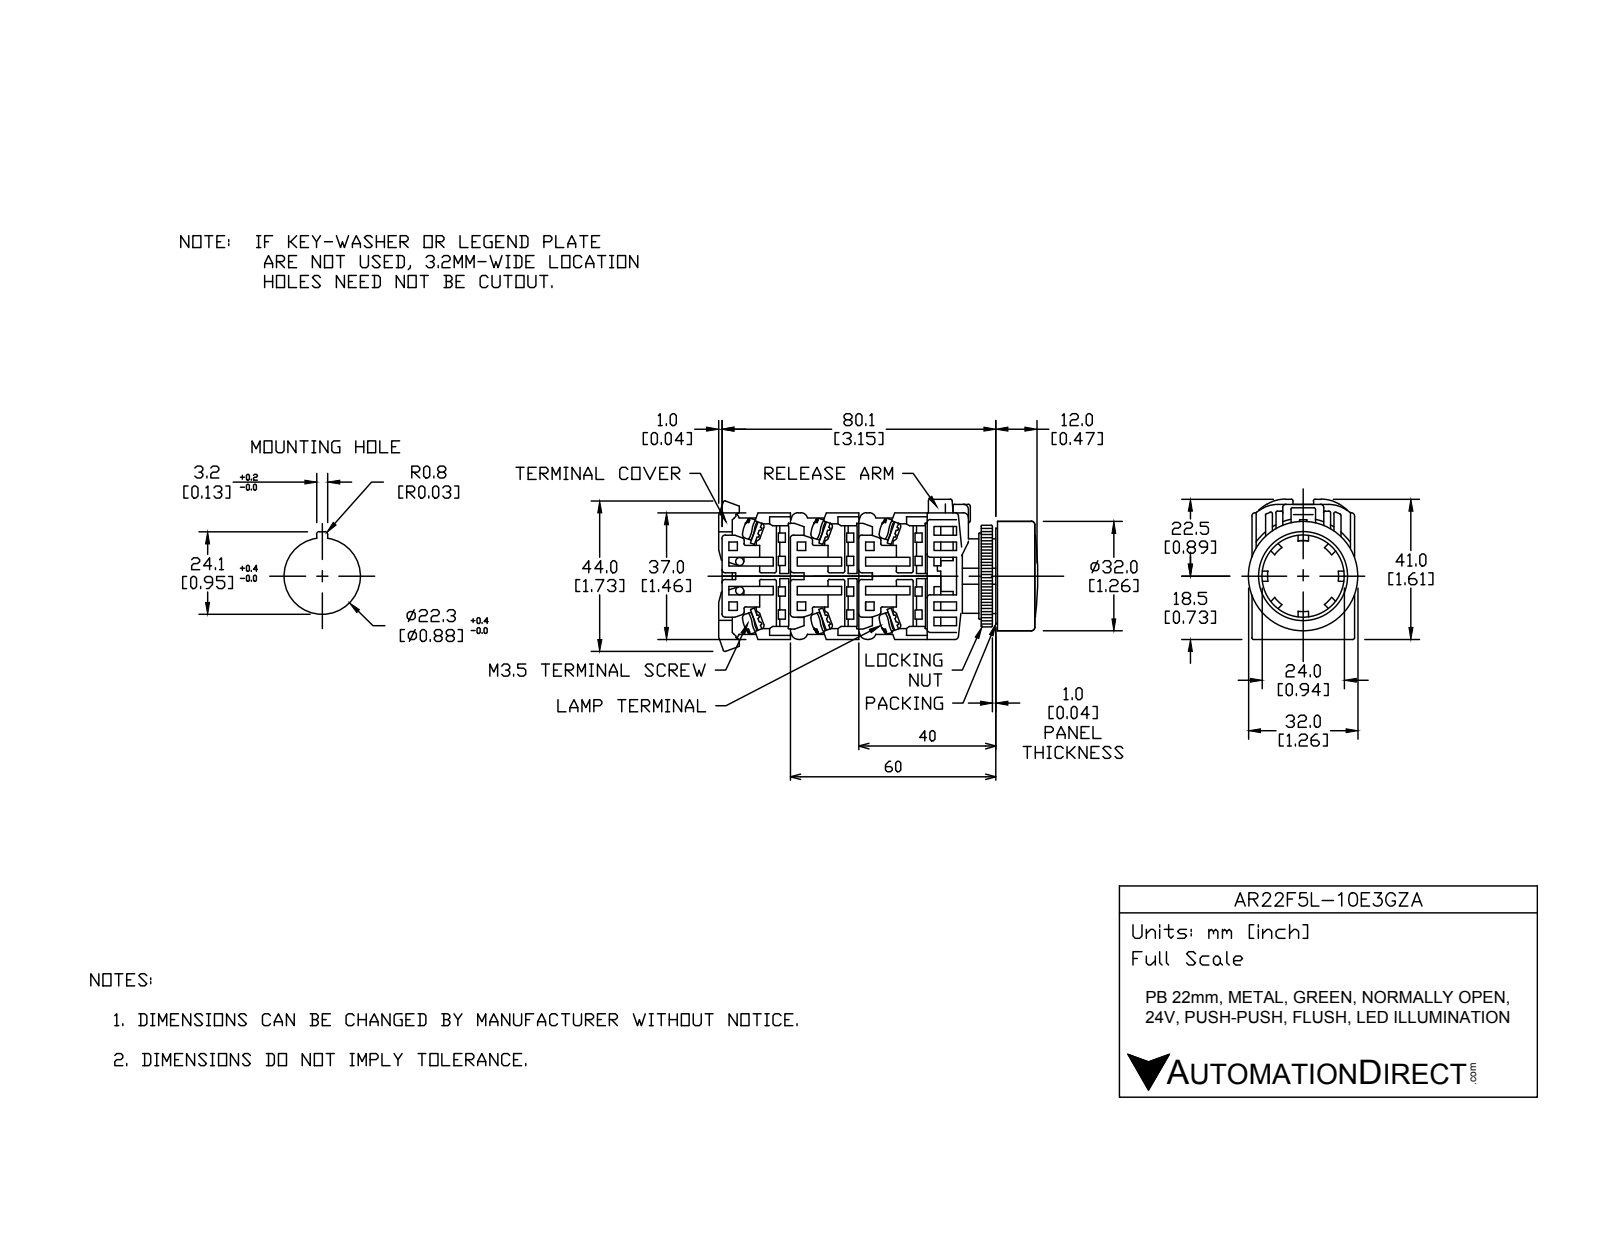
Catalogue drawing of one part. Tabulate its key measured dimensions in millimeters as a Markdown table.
| quantity | value |
| --- | --- |
| part name | AR22F5L-10E3GZA |
| STEP written by | SolidWorks 2017 (AUTOMOTIVE_DESIGN) |
| units | millimeters |
| bodies | 18 solids, 475 faces (329 planar, 111 cylindrical, 35 other) |
| overall size | 52.75 × 43.81 × 32 |
| volume | 36 367 mm³ |
| surface area | 24 064 mm² |
| round holes (diameter × count) | 21.8 × 1, 22 × 1, 25 × 1, 31 × 1 |
| round bosses / shafts (diameter × count) | 5 × 4, 32 × 1, 30.5 × 1, 29.8 × 1, 24 × 1, 23.8 × 1, 21.75 × 1, 17 × 1 |
| partial cylindrical surfaces (radius × count) | 0.5 × 39, 1.75 × 8, 5 × 4, 4 × 2, 16.59 × 1, 17.59 × 1 |
| main face-to-face distances | 1, 18, 28.5, 48.5, 20, 29, 3, 2, 21, 0.5 |
